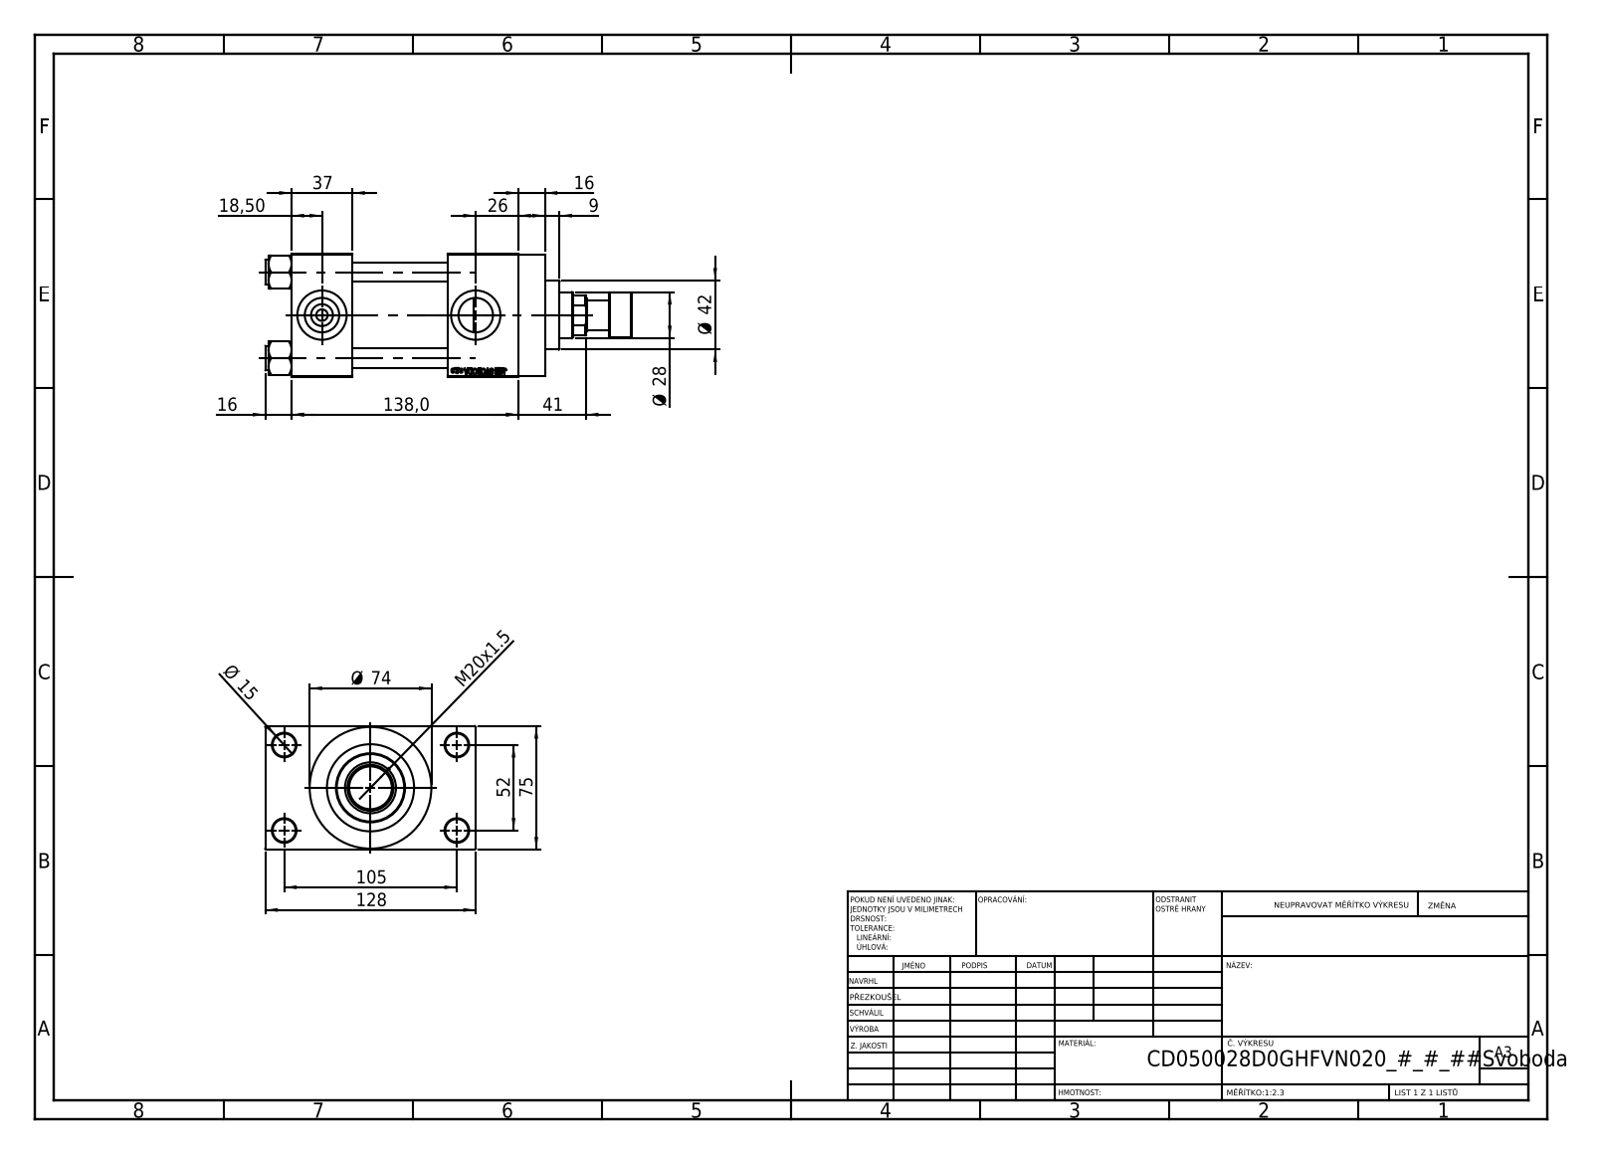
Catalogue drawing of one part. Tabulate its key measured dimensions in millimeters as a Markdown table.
| quantity | value |
| --- | --- |
| part name | V215CD_VC_A; V215CD_VCP_D; V215CR_ROD_END_F; V215CD_NUT_M5_D (+2 more) |
| STEP written by | SolidWorks 2019 (CONFIG_CONTROL_DESIGN) |
| units | millimeters |
| bodies | 12 solids, 1117 faces (501 planar, 92 cylindrical, 524 other) |
| overall size | 223 × 128 × 75 |
| volume | 817 817 mm³ |
| surface area | 173 865 mm² |
| round holes (diameter × count) | 12 × 4, 14 × 4, 7 × 2, 20.96 × 2, 30 × 2, 18.5 × 1, 28 × 1, 31 × 1, 41 × 1, 50 × 1, 53 × 1 |
| round bosses / shafts (diameter × count) | 15 × 4, 74 × 1, 56 × 1, 42 × 1, 27 × 1, 18 × 1 |
| main face-to-face distances | 75, 58, 37, 95, 26.5, 138, 101, 43, 101.5, 16 |
| hole center spacings | 26.35, 36.98, 52.3, 58.43, 58.59, 78.65, 94.37, 52 |
